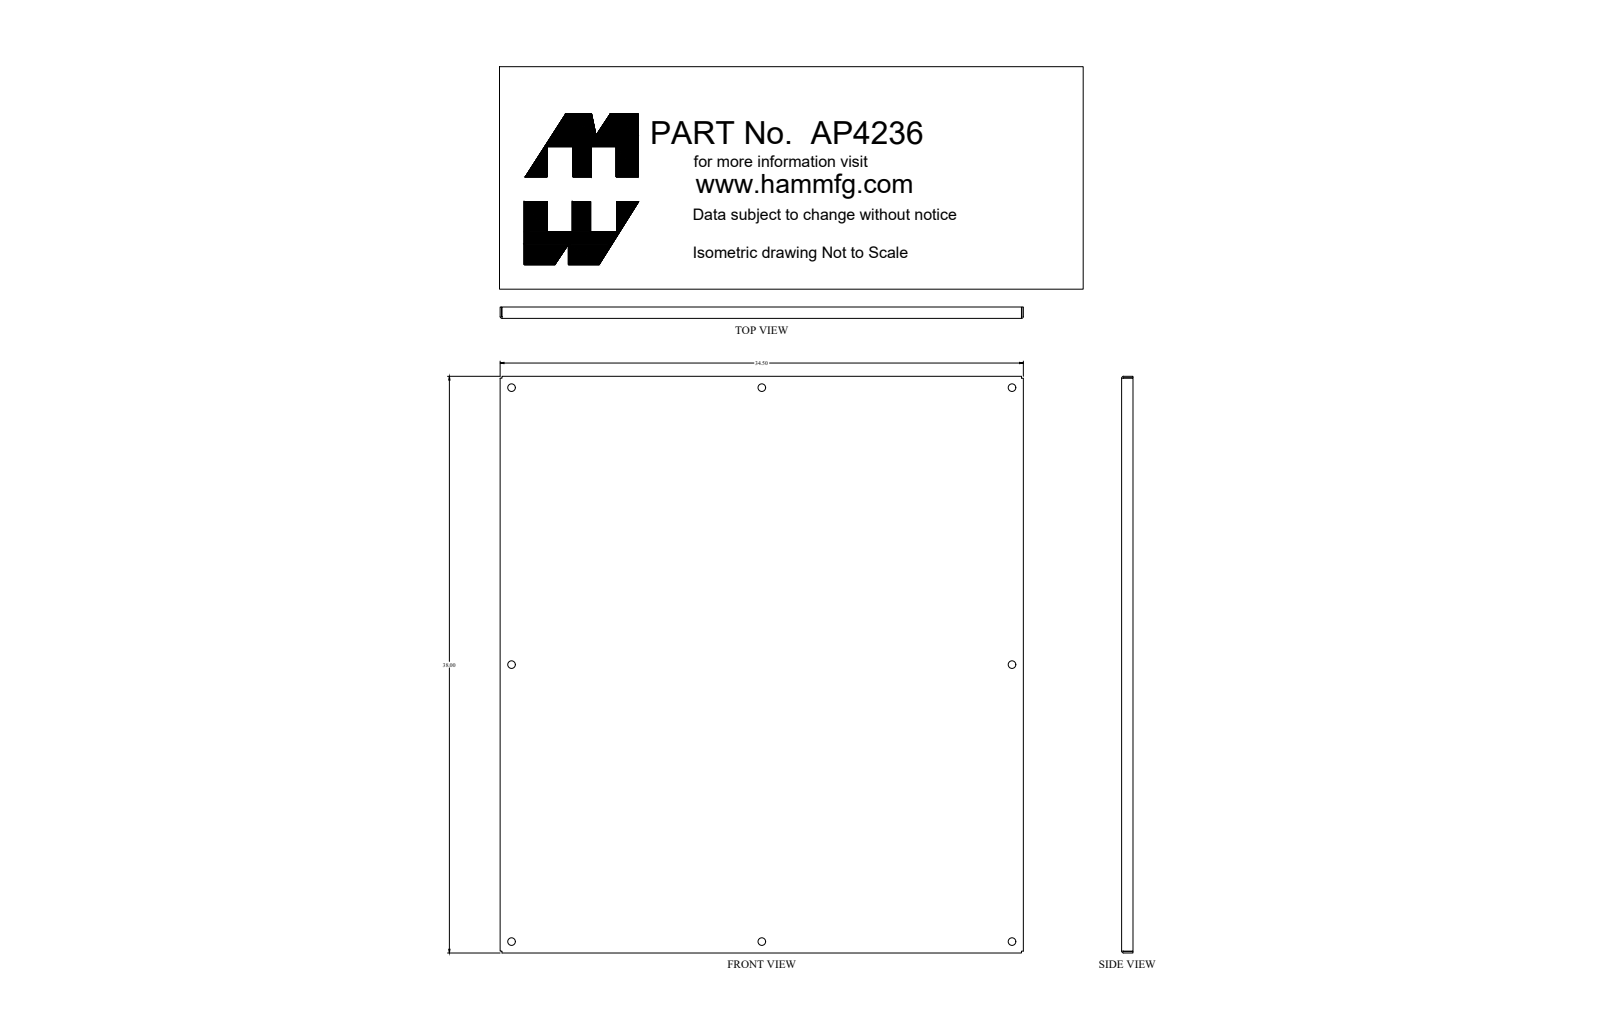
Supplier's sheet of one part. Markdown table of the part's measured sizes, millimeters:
| quantity | value |
| --- | --- |
| part name | AP4236_Default |
| STEP written by | SolidWorks 2019 (CONFIG_CONTROL_DESIGN) |
| units | millimeters |
| bodies | 1 solid, 46 faces (22 planar, 24 cylindrical, 0 other) |
| overall size | 965.2 × 876.3 × 19.1 |
| volume | 2 178 000 mm³ |
| surface area | 1 815 000 mm² |
| round holes (diameter × count) | 12.7 × 8 |
| partial cylindrical surfaces (radius × count) | 0.8 × 4, 3.2 × 4 |
| main face-to-face distances | 2.4, 873.9, 962.8, 871.5, 876.3, 965.2, 960.4, 19.1, 16.6, 3.2 |
| hole center spacings | 419.1, 463.5, 624.9, 957.8, 1017.4, 838.1, 927, 1249.8 |
